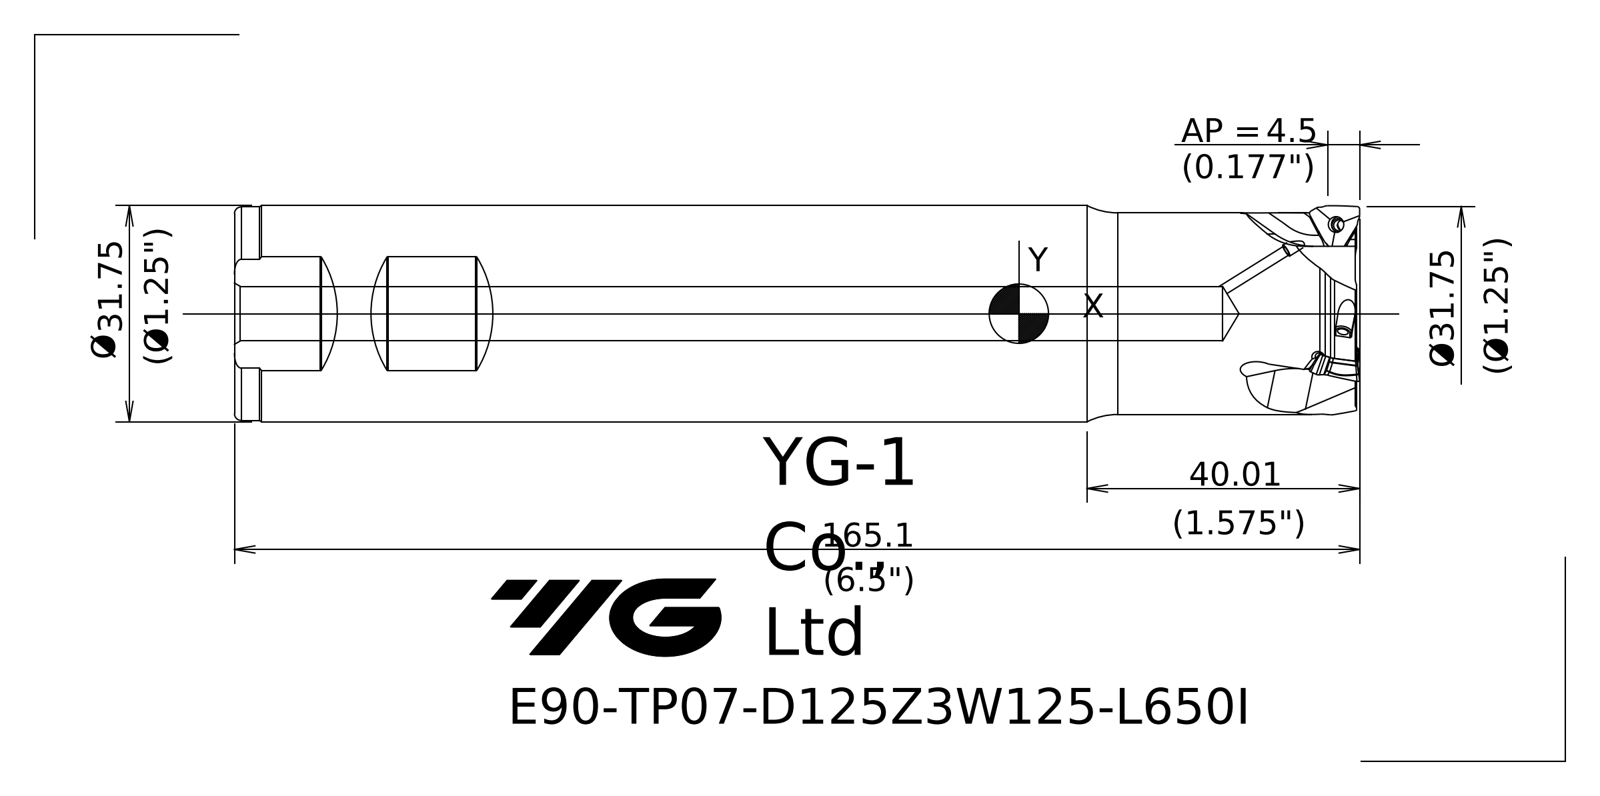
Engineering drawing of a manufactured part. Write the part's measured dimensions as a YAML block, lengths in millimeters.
part_name: "10224A58D494yyhb"
step_written_by: "SIEMENS PLM Software NX 10.0 (AP203_CONFIGURATION_CONTROLLED_3D_DESIGN_OF_MECHANICAL_PARTS_AND_ASSEMBLIES_MIM_LF)"
units: millimeters
bodies: {solids: 1, faces: 51, planar: 8, cylindrical: 8, other: 35}
overall_size: [165.1, 31.81, 31.81]
volume: 118200
surface_area: 23146
round_holes:
  - {diameter: 1.5, count: 1}
  - {diameter: 8, count: 1}
round_bosses_or_shafts:
  - {diameter: 31.75, count: 1}
  - {diameter: 31.35, count: 1}
  - {diameter: 29.6, count: 1}
partial_cylinders:
  - {radius: 0.3, count: 3}
face_to_face_distances: [164.45, 164.6, 16.13]
